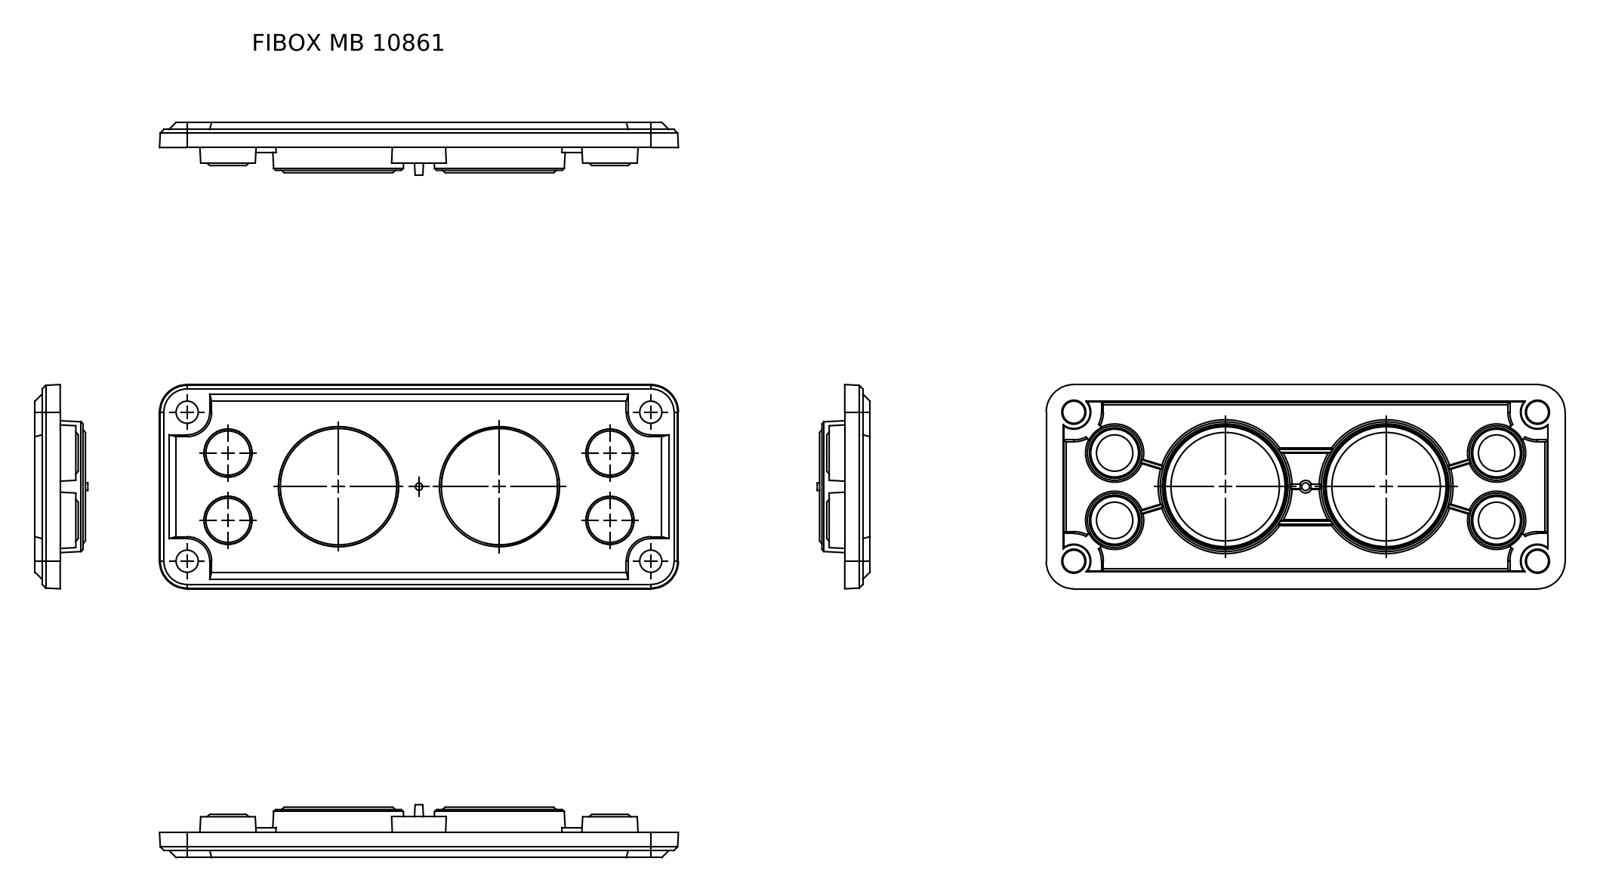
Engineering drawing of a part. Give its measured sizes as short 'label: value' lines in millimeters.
name: FIBOX MB10861
written by: SolidWorks 2014 (AUTOMOTIVE_DESIGN)
unit: mm
bodies: 1 solid, 215 faces (113 planar, 14 cylindrical, 88 other)
size: 216 × 85 × 22
volume: 93 508 mm³; area: 66 876 mm²
holes: 4× ⌀18.38, 1× ⌀48.3, 1× ⌀48.38, 1× ⌀50
face distances: 10.5, 2.5, 2, 3, 19, 8, 8.5, 16.5, 16, 21
hole spacings: 48.08, 113.86, 28, 159, 161.45, 67
